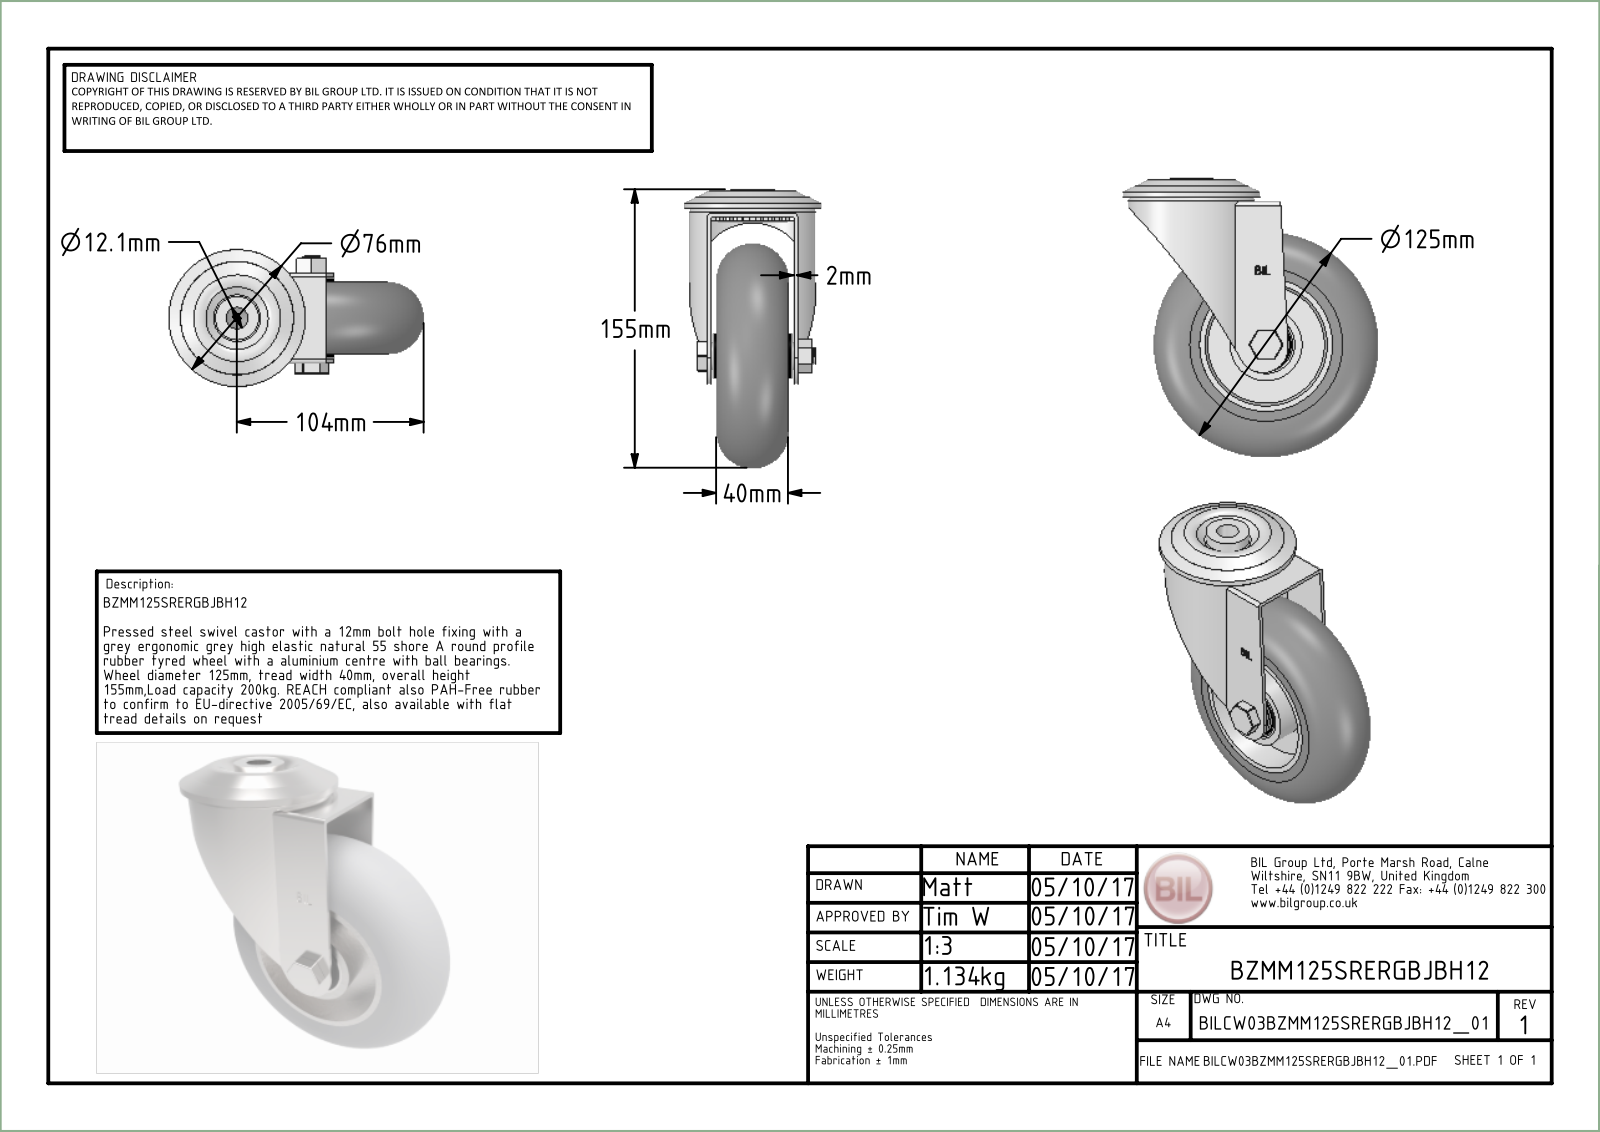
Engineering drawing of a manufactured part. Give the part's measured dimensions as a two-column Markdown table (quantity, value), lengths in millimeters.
| quantity | value |
| --- | --- |
| part name | BZMM125SRERGBJBH12 v2; BZMM125ASBH12 v1; ZINC PLATED, PRESSED STEEL HEAD; ZINC PLATED, PRESSED STEEL FORKS (+8 more) |
| STEP written by | Autodesk Translation Framework v13.20.0.188 (AP242_MANAGED_MODEL_BASED_3D_ENGINEERING_MIM_LF) |
| units | millimeters |
| bodies | 39 solids, 1089 faces (369 planar, 185 cylindrical, 535 other) |
| overall size | 155 × 142 × 76 |
| volume | 417 480 mm³ |
| surface area | 138 590 mm² |
| round holes (diameter × count) | 10 × 1, 10.2 × 1, 12 × 1, 12.2 × 1, 15 × 1, 15.75 × 1, 20.5 × 1, 26 × 1, 26.8 × 1, 28 × 1, 28.2 × 1, 32 × 1 |
| round bosses / shafts (diameter × count) | 70 × 1, 49.5 × 1, 40 × 1, 38 × 1, 25 × 1, 24 × 1, 21.5 × 1, 21.31 × 1 |
| partial cylindrical surfaces (radius × count) | 0.5 × 18, 0.75 × 12, 1.25 × 4, 2.5 × 2, 11.4 × 1, 12.9 × 1, 13.5 × 1, 253.62 × 1 |
| main face-to-face distances | 2.5, 45, 5, 47.5, 42.5, 15.75, 20.75, 29.25, 18.25, 26.75 |
